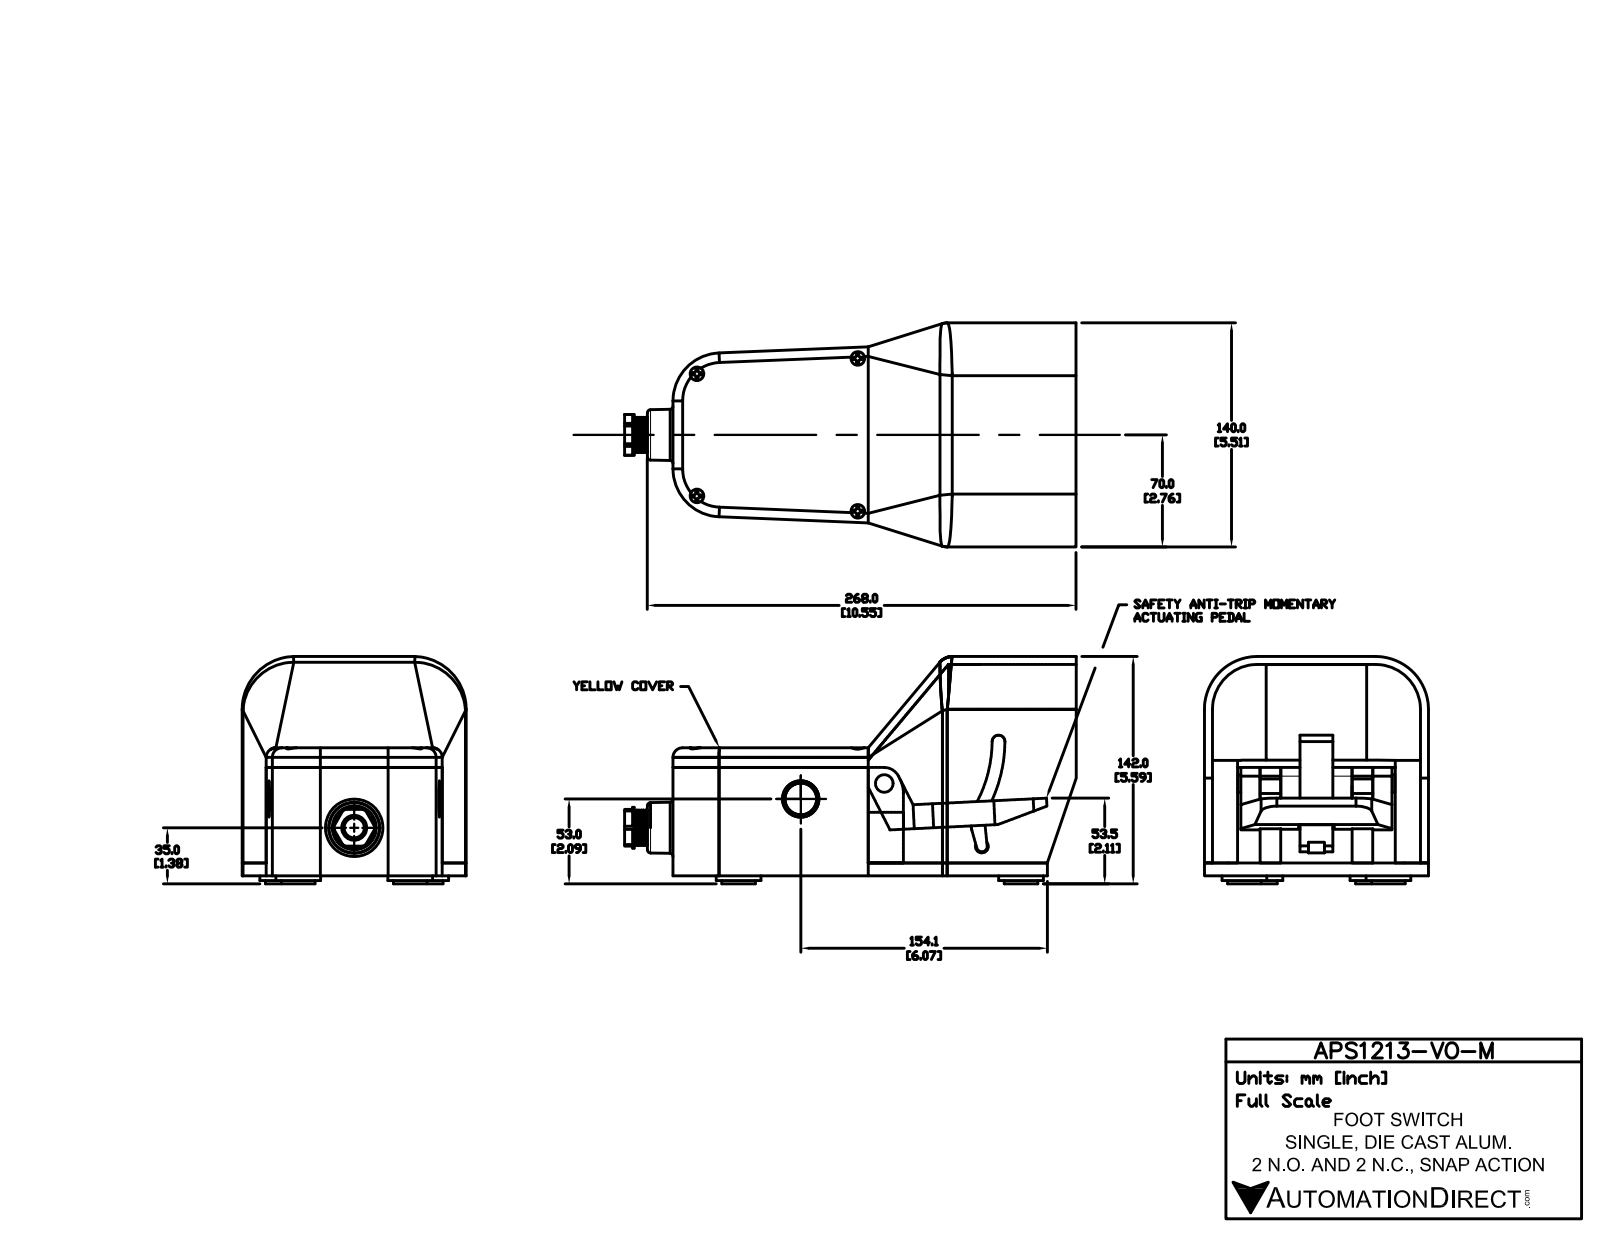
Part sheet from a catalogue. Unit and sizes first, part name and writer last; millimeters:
Units: millimetres
Overall size (bounding box): 282.25 × 142 × 140
Round holes (diameter × count): ⌀8.5 ×4, ⌀22.75 ×2, ⌀12.65 ×1, ⌀15.6 ×1
Round bosses / shafts (diameter × count): ⌀28 ×4, ⌀21 ×4, ⌀19.87 ×2, ⌀25.5 ×1, ⌀22 ×1, ⌀11 ×1
Partial cylindrical surfaces — rounded edges, fillets, slot ends (radius × count): R1 ×16, R10 ×7, R5.99 ×3, R20 ×2, R28 ×2, R30 ×2, R33 ×2, R3.35 ×1
Main face-to-face distances: 5, 135, 8, 59.64, 67.67, 59.67, 67.64, 140, 80, 72
Hole centre spacings: 101, 132.24, 76.3, 95.5
Volume: 1 553 000 mm³ · Surface area: 272 464 mm²
Bodies: 19 solids, 379 faces (220 planar, 103 cylindrical, 56 other)
Part name (STEP PRODUCT): APS1213-V0-M
STEP written by: SolidWorks 2015 (AUTOMOTIVE_DESIGN)
